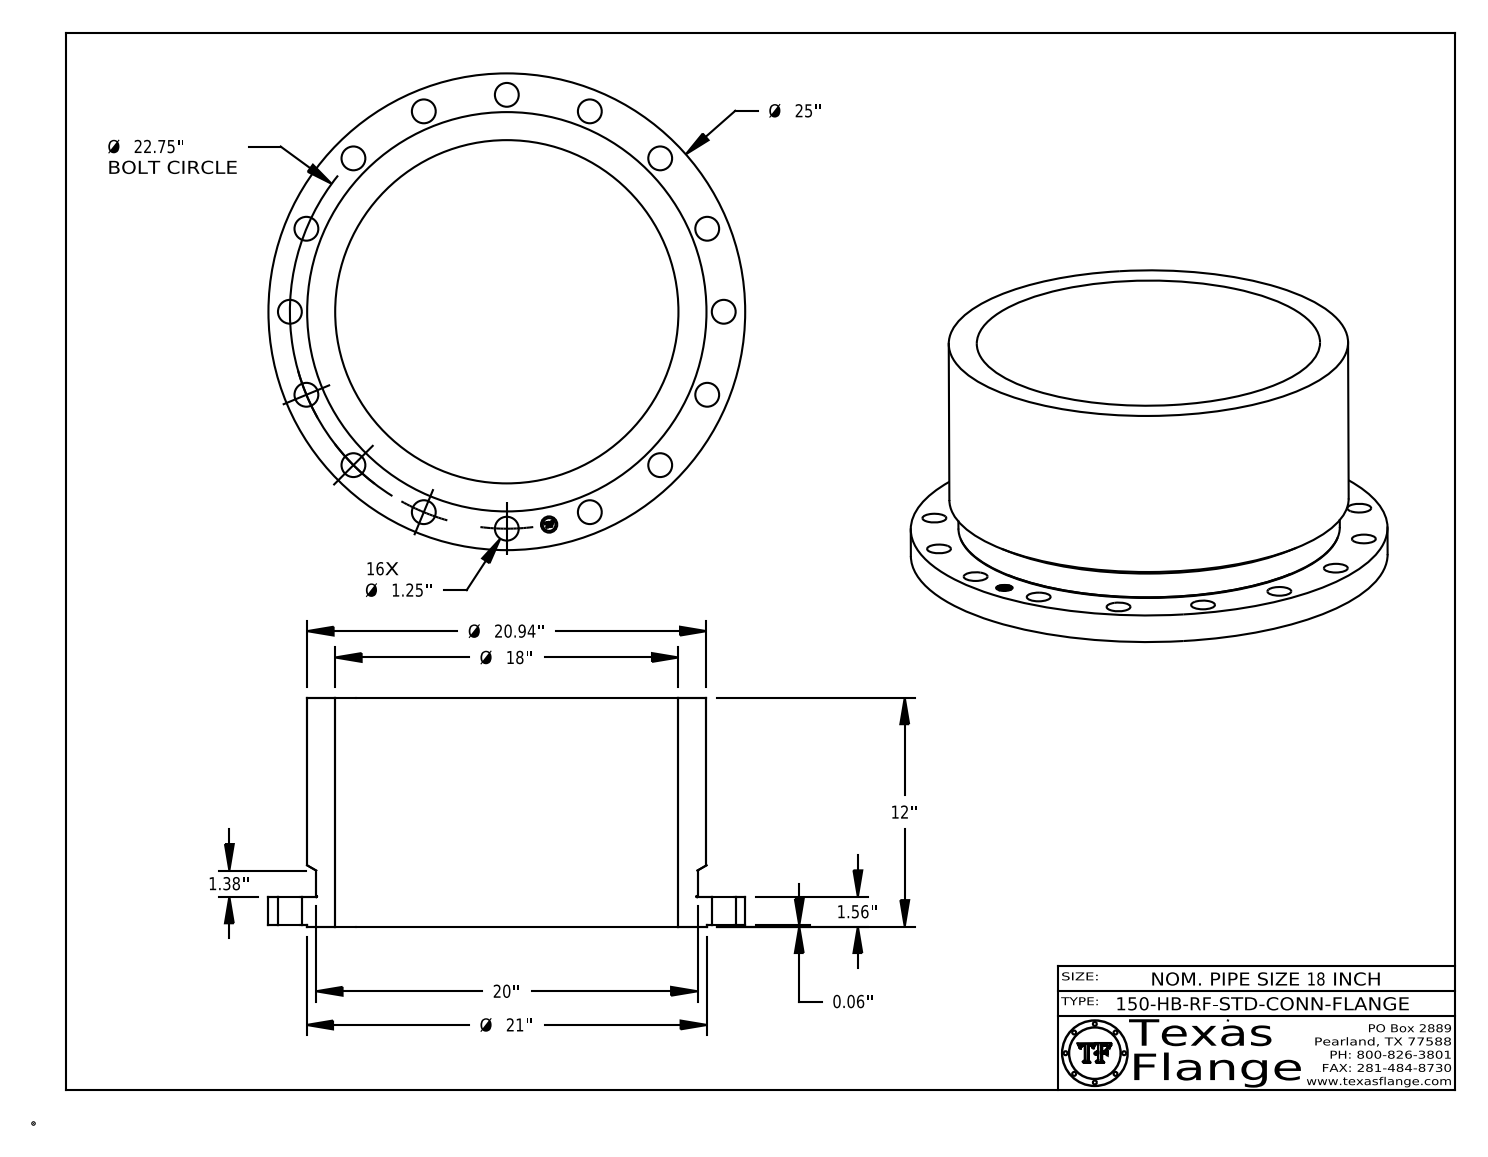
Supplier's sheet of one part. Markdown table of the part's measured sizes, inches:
| quantity | value |
| --- | --- |
| part name | 18-150-HB-RF-STD-CONN-FLANGE |
| STEP written by | CATIA V5 STEP AP214 (AUTOMOTIVE_DESIGN) |
| units | inches |
| bodies | 1 solid, 437 faces (369 planar, 62 cylindrical, 6 other) |
| overall size | 25 × 25 × 12 |
| volume | 1 223 in³ |
| surface area | 2 060 in² |
| round holes (diameter × count) | 1.25 × 16, 0.85 × 1, 18 × 1 |
| round bosses / shafts (diameter × count) | 0.051 × 8, 25 × 1, 21 × 1, 20.94 × 1, 20 × 1, 0.67 × 1 |
| main face-to-face distances | 1.498, 0.063, 1.56, 12, 11.937, 10.44, 1.555, 1.493, 10.445, 0.254 |
| hole center spacings | 12.639, 22.313, 11.375, 8.706, 16.087, 21.019, 4.438, 4.439 |
